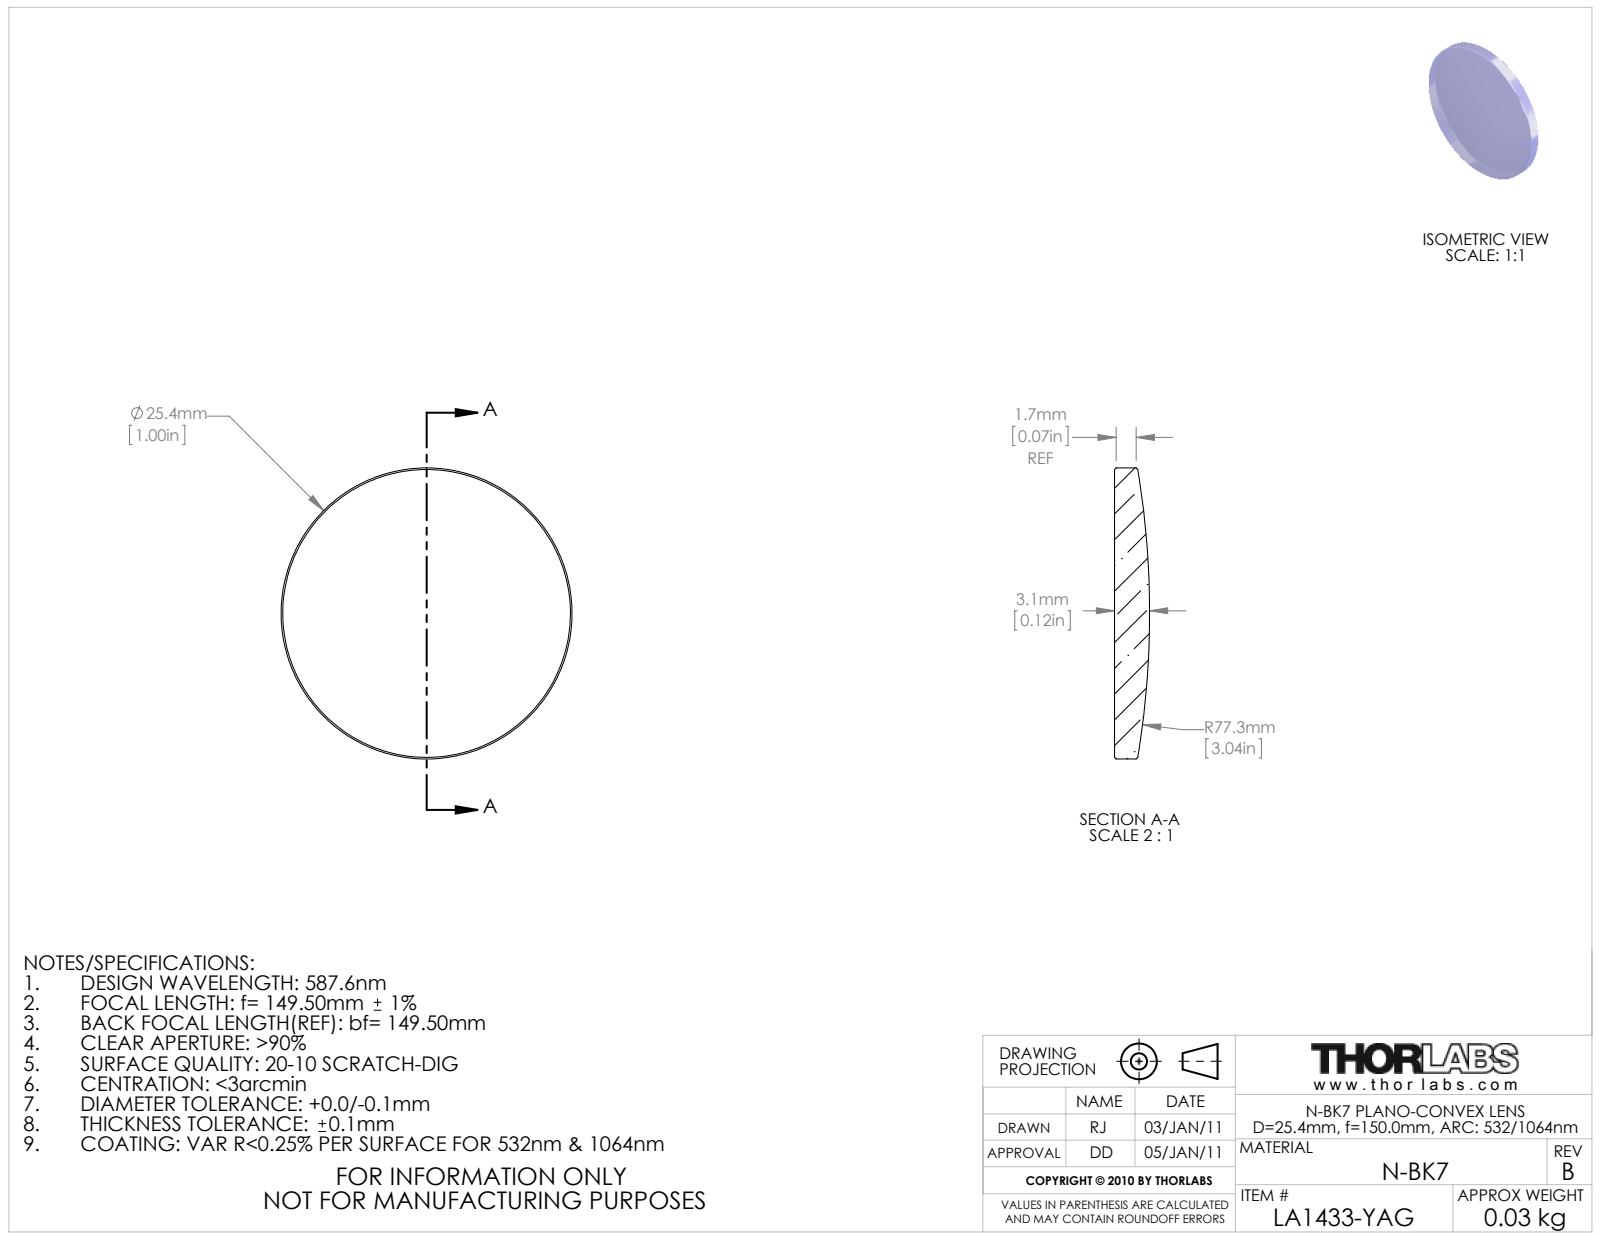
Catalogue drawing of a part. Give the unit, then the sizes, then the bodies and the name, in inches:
Units: inches
Overall size (bounding box): 1 × 1 × 0.12
Round bosses / shafts (diameter × count): ⌀1 ×1
Bodies: 0 solids, 9 faces (1 planar, 2 cylindrical, 6 other)
Part name (STEP PRODUCT): 21794-E0W
STEP written by: SolidWorks 2011 (AUTOMOTIVE_DESIGN)
